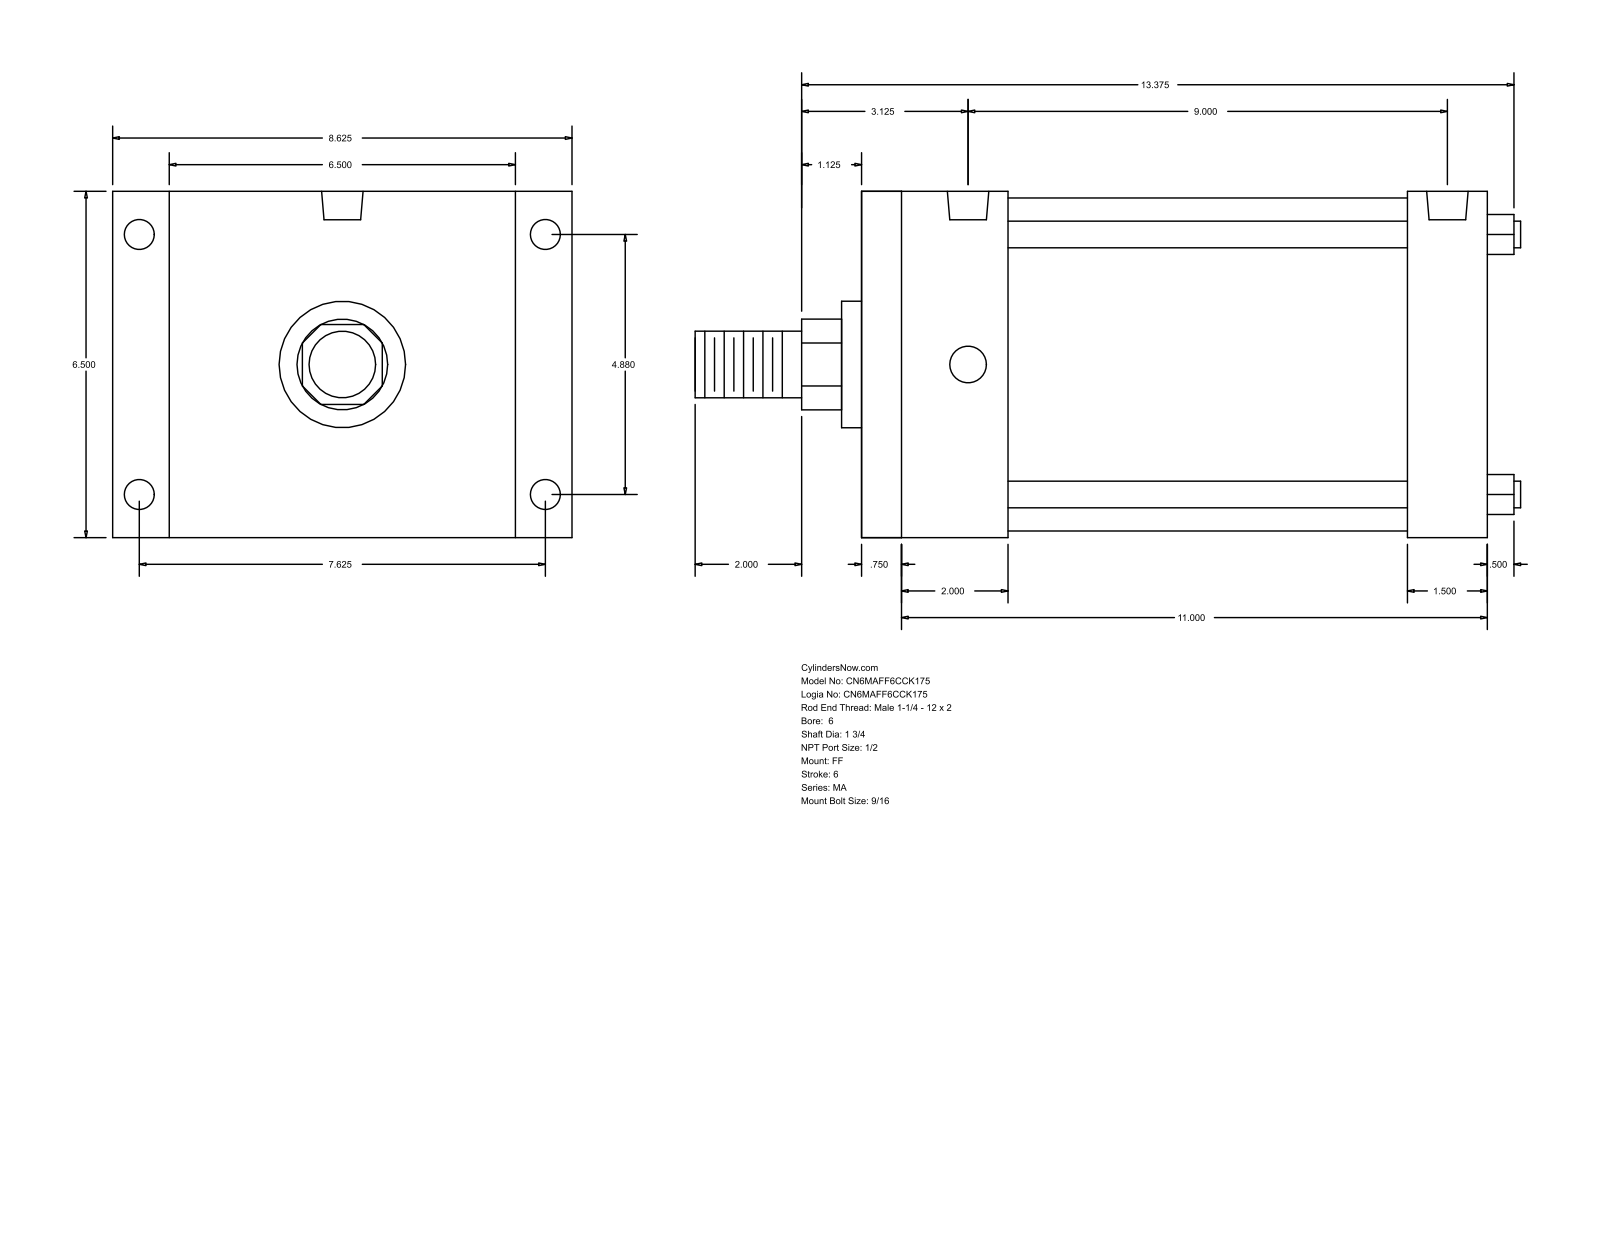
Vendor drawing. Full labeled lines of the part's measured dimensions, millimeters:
Part name (STEP PRODUCT): MA_FF__0600_1.75
STEP written by: GSSL Pune (CONFIG_CONTROL_DESIGN)
Units: millimetres
Bodies: 0 solids, 92 faces (64 planar, 28 cylindrical, 0 other)
Overall size (bounding box): 393.7 × 219.07 × 165.1
Round holes (diameter × count): ⌀14.29 ×4, ⌀17.46 ×4, ⌀19.77 ×2
Round bosses / shafts (diameter × count): ⌀12.7 ×4, ⌀158.75 ×1, ⌀60.33 ×1, ⌀44.45 ×1, ⌀31.75 ×1
Partial cylindrical surfaces — rounded edges, fillets, slot ends (radius × count): R21.63 ×1
Main face-to-face distances: 165.1, 298.45, 19.05, 279.4, 50.8, 69.85, 241.31, 228.6, 260.36, 190.51
Hole centre spacings: 123.96, 193.68, 228.6, 229.95
